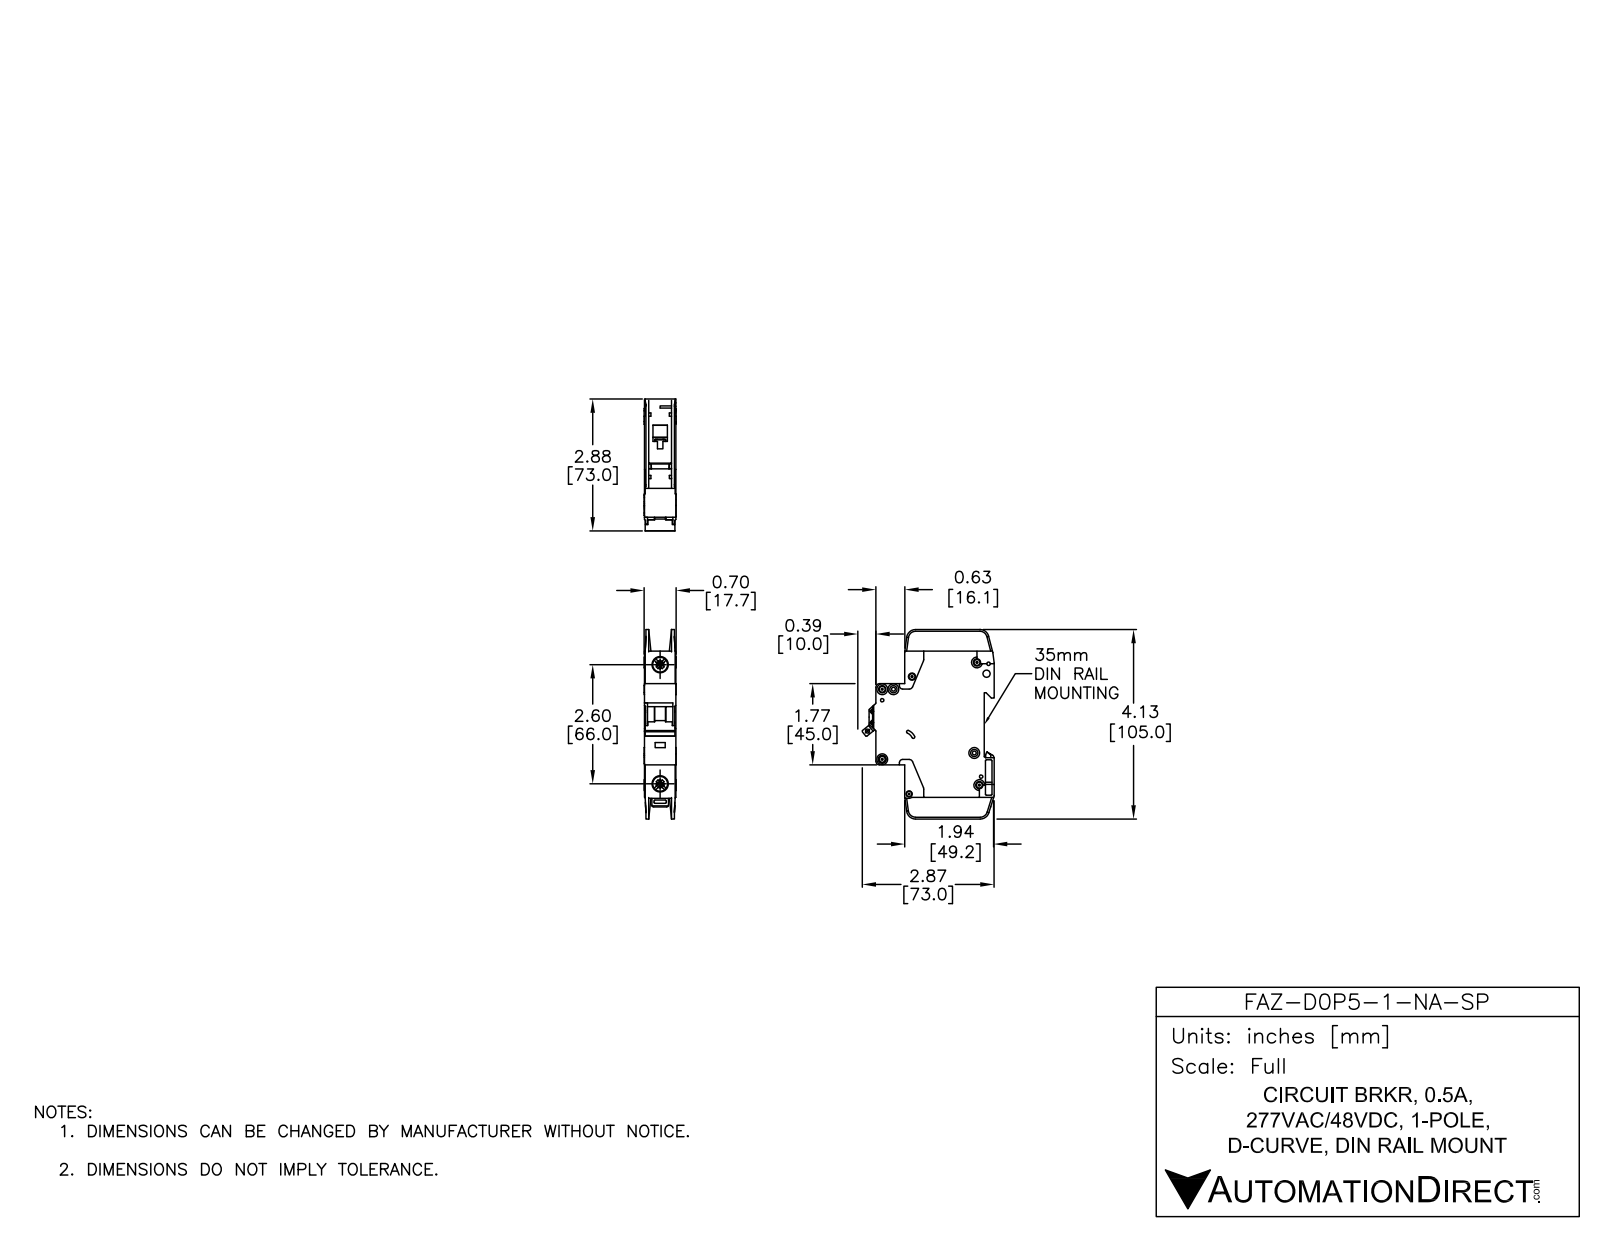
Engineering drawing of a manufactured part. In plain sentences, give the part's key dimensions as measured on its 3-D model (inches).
The part is named "FAZ-D0P5-1-NA-SP". Its 3-D file was written by "SolidWorks 2014 (AUTOMOTIVE_DESIGN)". It is 3 solids with 784 faces: 409 planar, 263 cylindrical and 112 other. Overall it measures 4.134 by 2.876 by 0.697 inches. Its volume is 4.741 cubic inches and its surface area 38.35 square inches. Round holes: 7 of diameter 0.142, 2 of diameter 0.043, 2 of diameter 0.059, 2 of diameter 0.157, 2 of diameter 0.281, 2 of diameter 0.323, 1 of diameter 0.075, 1 of diameter 0.085, 1 of diameter 0.087, 1 of diameter 0.1, 1 of diameter 0.13, 1 of diameter 0.134. Round bosses or shafts: 7 of diameter 0.236, 1 of diameter 0.098. Partial cylindrical surfaces (rounded edges, fillets, slot ends): 29 of radius 0.01, 18 of radius 0.02, 10 of radius 0.039, 10 of radius 0.079, 5 of radius 0.197, 4 of radius 0.157, 3 of radius 0.071, 2 of radius 0.008. The main face-to-face distances are 0.689, 0.593, 0.028, 0.096, 0.069, 0.62, 0.524, 0.551, 0.496, 0.079. The hole center spacings are 0.244, 0.204, 0.24, 0.322, 0.337, 0.343, 0.437, 0.49.
